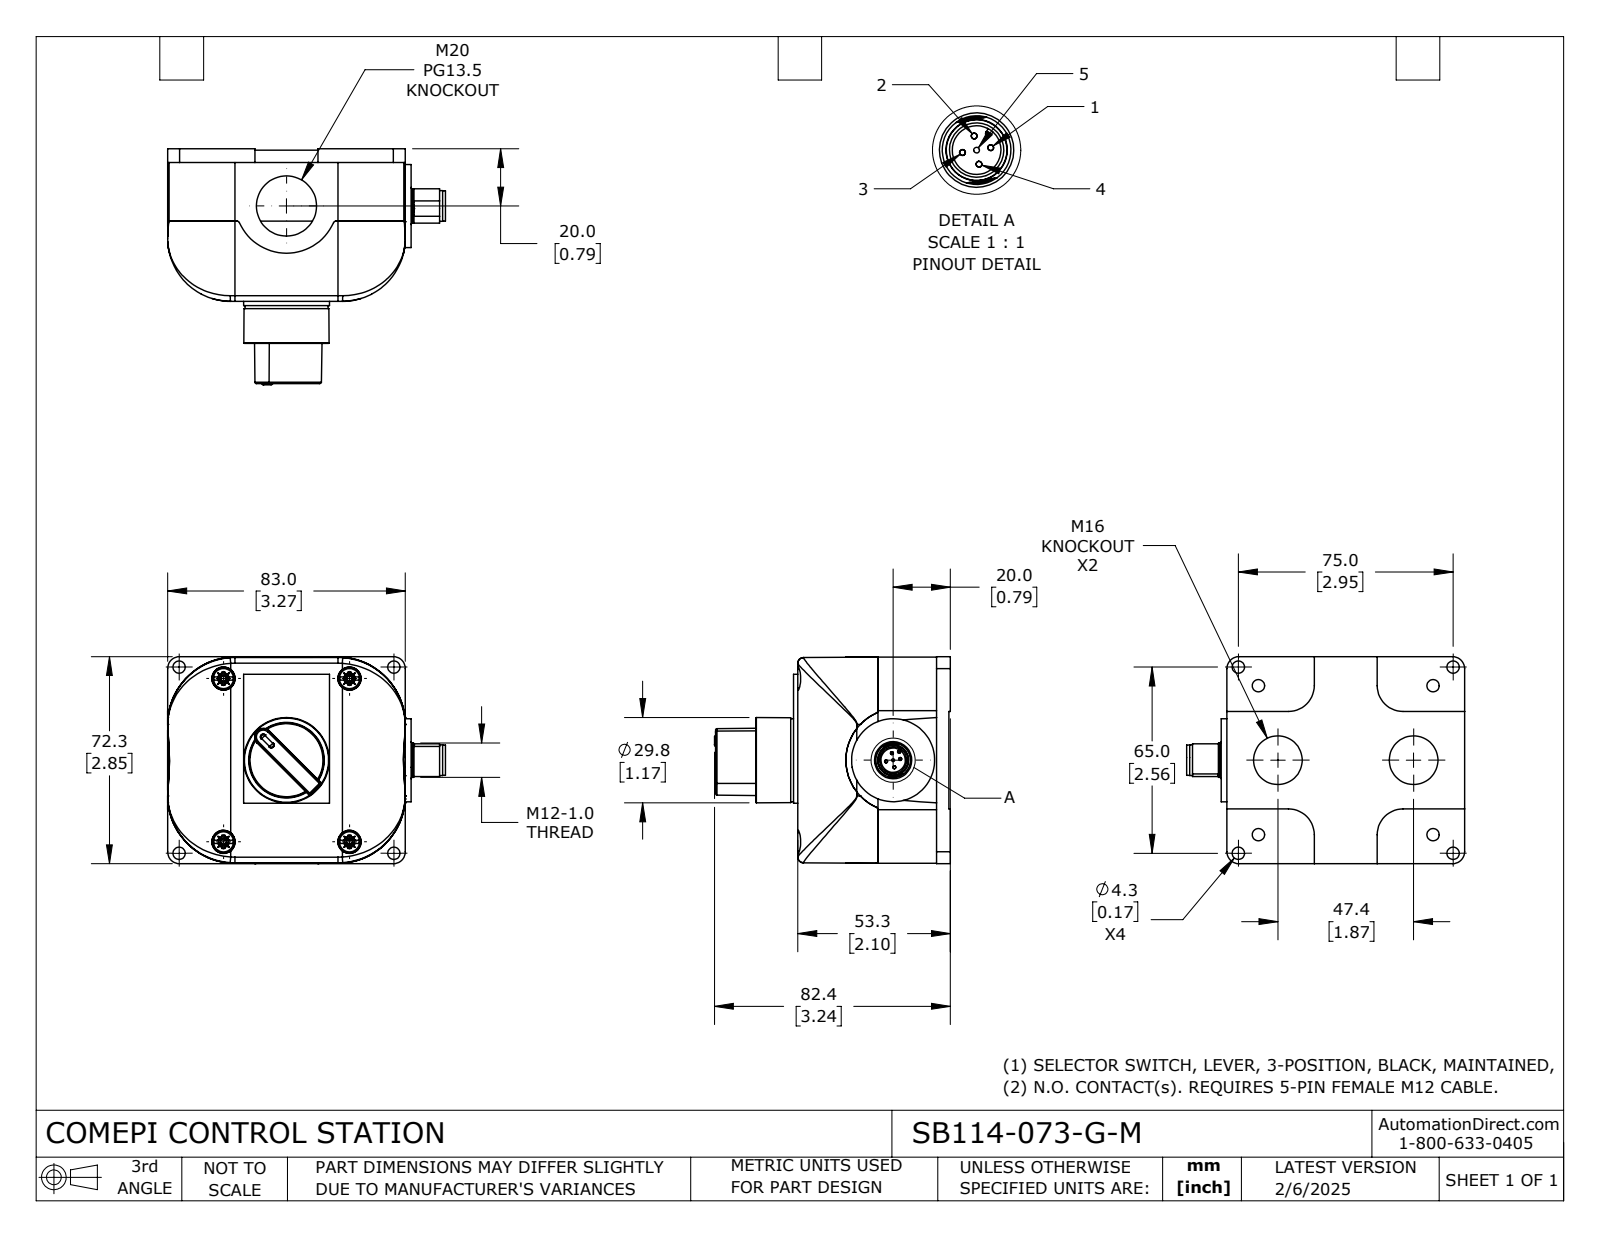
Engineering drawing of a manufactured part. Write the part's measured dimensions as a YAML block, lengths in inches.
part_name: "SB114-073-G-M"
step_written_by: "SolidWorks 2024 (CONFIG_CONTROL_DESIGN)"
units: inches
bodies: {solids: 11, faces: 824, planar: 402, cylindrical: 288, other: 134}
overall_size: [3.821, 3.244, 2.846]
volume: 13.53
surface_area: 100.8
round_holes:
  - {diameter: 0.169, count: 8}
  - {diameter: 0.04, count: 4}
  - {diameter: 0.067, count: 4}
  - {diameter: 0.087, count: 4}
  - {diameter: 0.323, count: 4}
  - {diameter: 0.669, count: 2}
  - {diameter: 0.827, count: 2}
  - {diameter: 0.098, count: 1}
  - {diameter: 0.335, count: 1}
  - {diameter: 0.5, count: 1}
  - {diameter: 0.551, count: 1}
  - {diameter: 0.75, count: 1}
round_bosses_or_shafts:
  - {diameter: 0.039, count: 5}
  - {diameter: 0.276, count: 4}
  - {diameter: 0.085, count: 4}
  - {diameter: 0.065, count: 4}
  - {diameter: 1.142, count: 2}
  - {diameter: 0.024, count: 2}
  - {diameter: 1.039, count: 1}
  - {diameter: 1.004, count: 1}
partial_cylinders:
  - {radius: 0.02, count: 8}
  - {radius: 0.039, count: 5}
  - {radius: 0.035, count: 4}
  - {radius: 0.079, count: 4}
  - {radius: 0.354, count: 4}
  - {radius: 0.38, count: 4}
  - {radius: 0.925, count: 4}
  - {radius: 0.01, count: 2}
face_to_face_distances: [2.079, 0.098, 0.976, 1.102, 0.878, 1.98, 0.118, 0.02, 0.996, 2.098]
hole_center_spacings: [0.376, 1.058, 1.39, 1.578, 1.954, 2.32, 2.367, 2.689]
